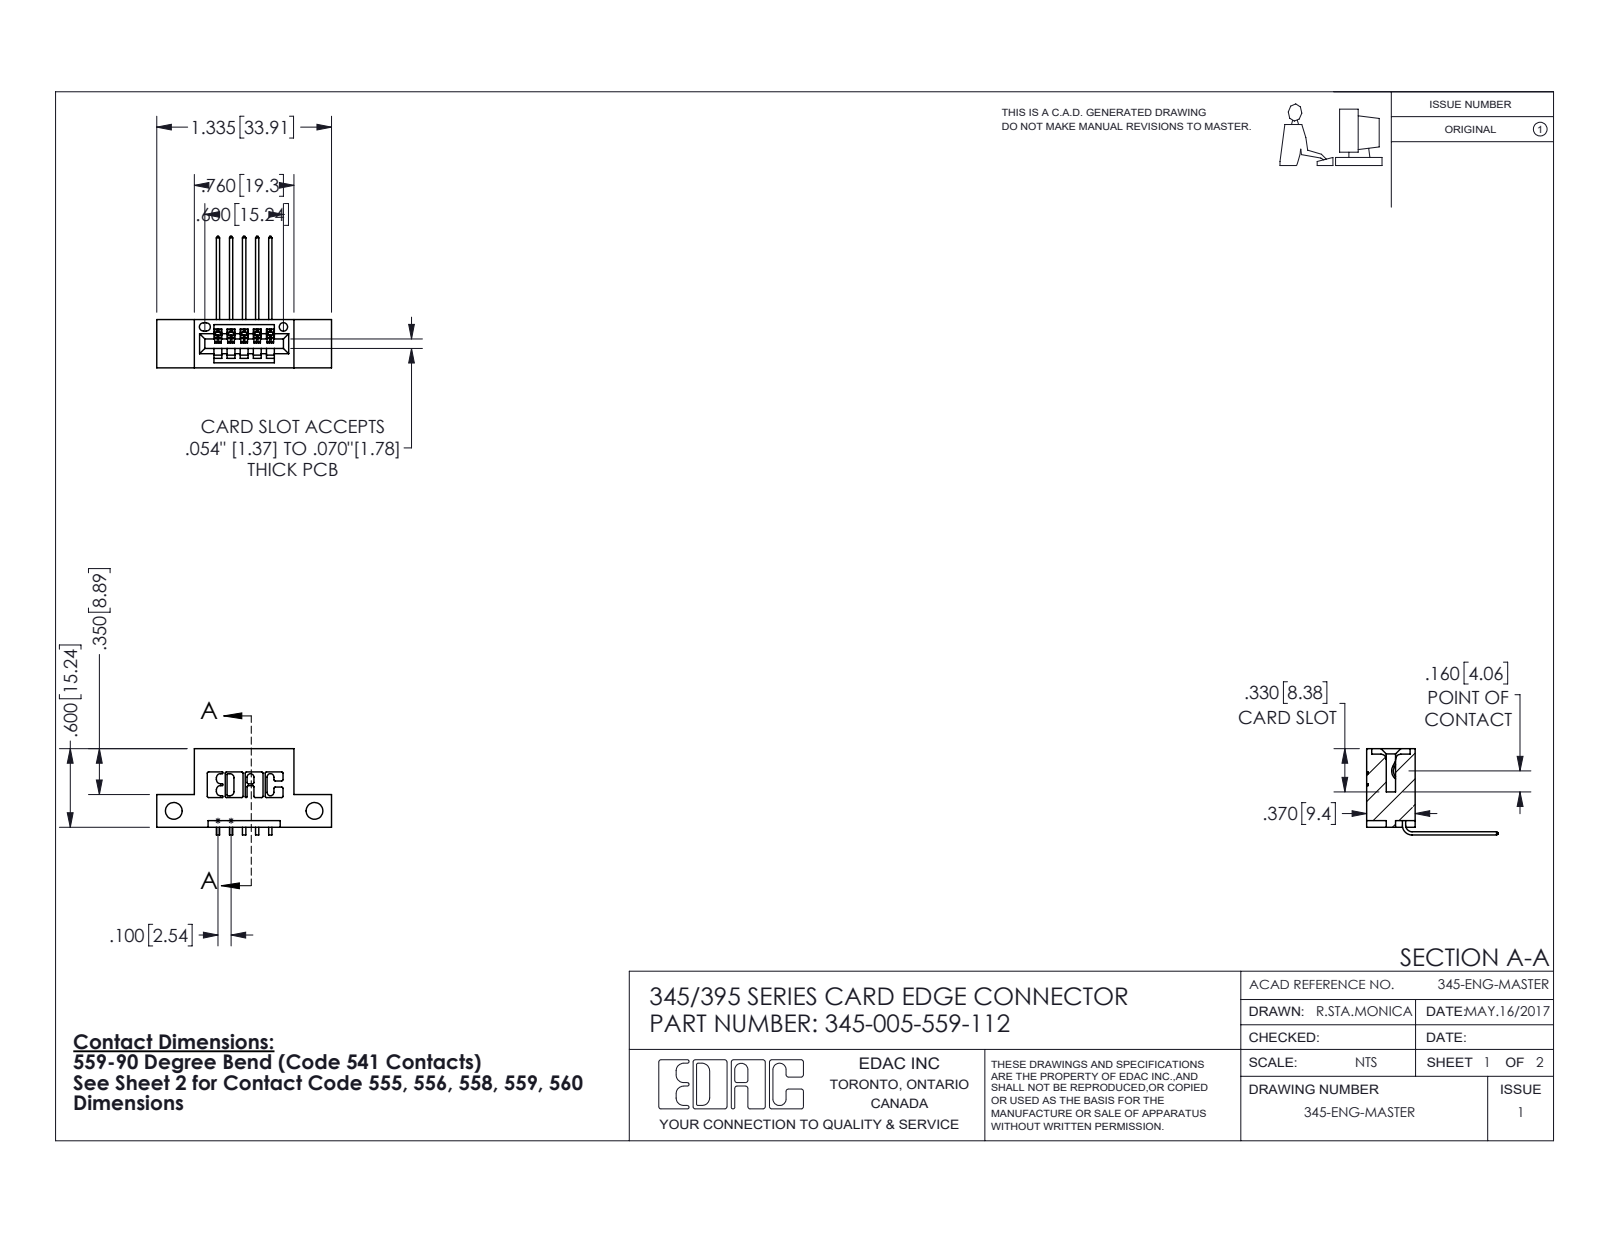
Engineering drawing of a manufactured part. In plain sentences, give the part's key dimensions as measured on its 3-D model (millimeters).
The part is named "345-005-559-112; 345-292-001_558 559 Tail - 1; 345 Part_Flush Mounting Lugs - Side Mount". Its 3-D file was written by "SolidWorks 2016 (CONFIG_CONTROL_DESIGN)". It is 6 solids with 426 faces: 290 planar, 136 cylindrical and 0 other. Overall it measures 33.9 by 25.5 by 16.7 millimeters. Its volume is 2 850 cubic millimeters and its surface area 3 236 square millimeters. Round holes: 2 of diameter 3.3, 1 of diameter 1.6. Partial cylindrical surfaces (rounded edges, fillets, slot ends): 22 of radius 0.3, 10 of radius 0.2, 6 of radius 0.2, 6 of radius 0.8, 3 of radius 0.7, 2 of radius 0.8, 2 of radius 1, 1 of radius 0.4. The main face-to-face distances are 5.1, 9.4, 2.5, 7.6, 1.8, 6.4, 1.5, 2.5, 6.9, 0.6. The hole center spacings are 27.3.
